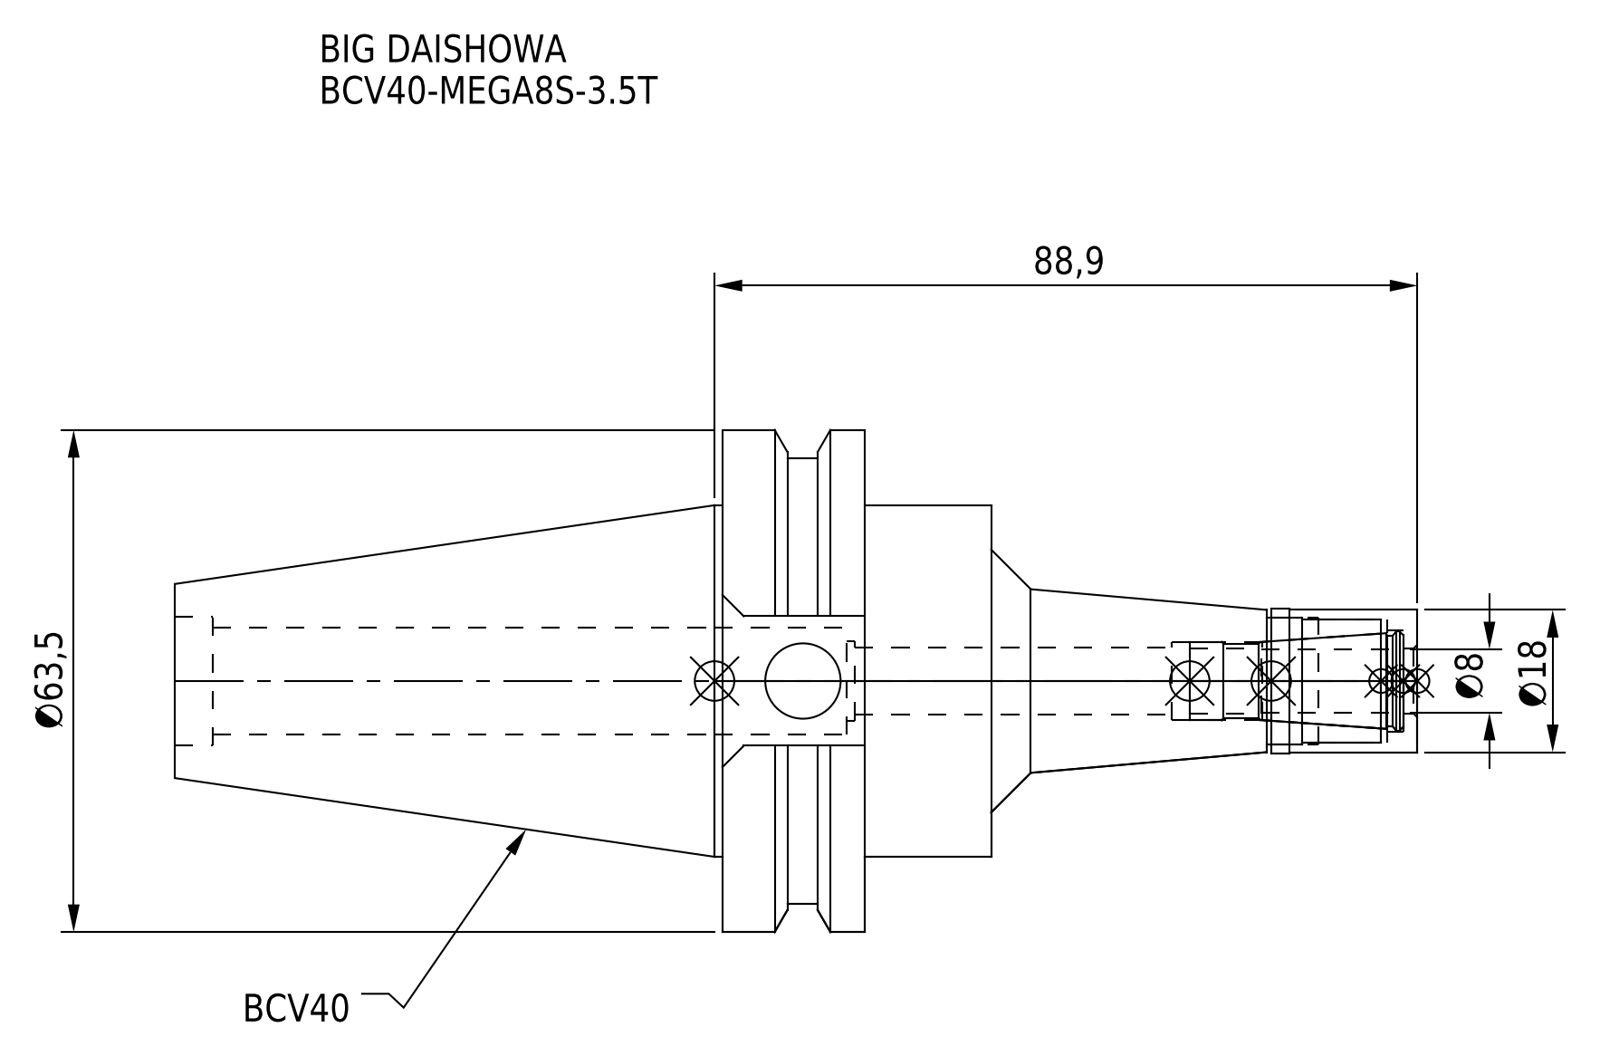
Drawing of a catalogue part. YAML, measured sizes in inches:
part_name: "MGN8S_1.stp; BCV40MS08035T-080_ASM.stp; DXF_TEMP_ASSY_ASM_4_ASM.stp; BCV40-MEGA8S-3_5T (+3 more)"
step_written_by: "SolidWorks 2019 (CONFIG_CONTROL_DESIGN)"
units: inches
bodies: {solids: 2, faces: 86, planar: 32, cylindrical: 40, other: 14}
overall_size: [6.187, 2.5, 2.415]
volume: 8.651
surface_area: 46
round_holes:
  - {diameter: 0.323, count: 1}
  - {diameter: 0.331, count: 1}
  - {diameter: 0.375, count: 1}
  - {diameter: 0.39, count: 1}
  - {diameter: 0.394, count: 1}
  - {diameter: 0.508, count: 1}
  - {diameter: 0.535, count: 1}
  - {diameter: 0.614, count: 1}
  - {diameter: 0.634, count: 1}
  - {diameter: 0.643, count: 1}
round_bosses_or_shafts:
  - {diameter: 2.5, count: 1}
  - {diameter: 2.219, count: 1}
  - {diameter: 1.75, count: 1}
  - {diameter: 0.72, count: 1}
  - {diameter: 0.709, count: 1}
face_to_face_distances: [0.711, 0.628, 1.339, 4.065, 3.437, 2.726, 1.872, 2.122, 2.75, 3.461]
